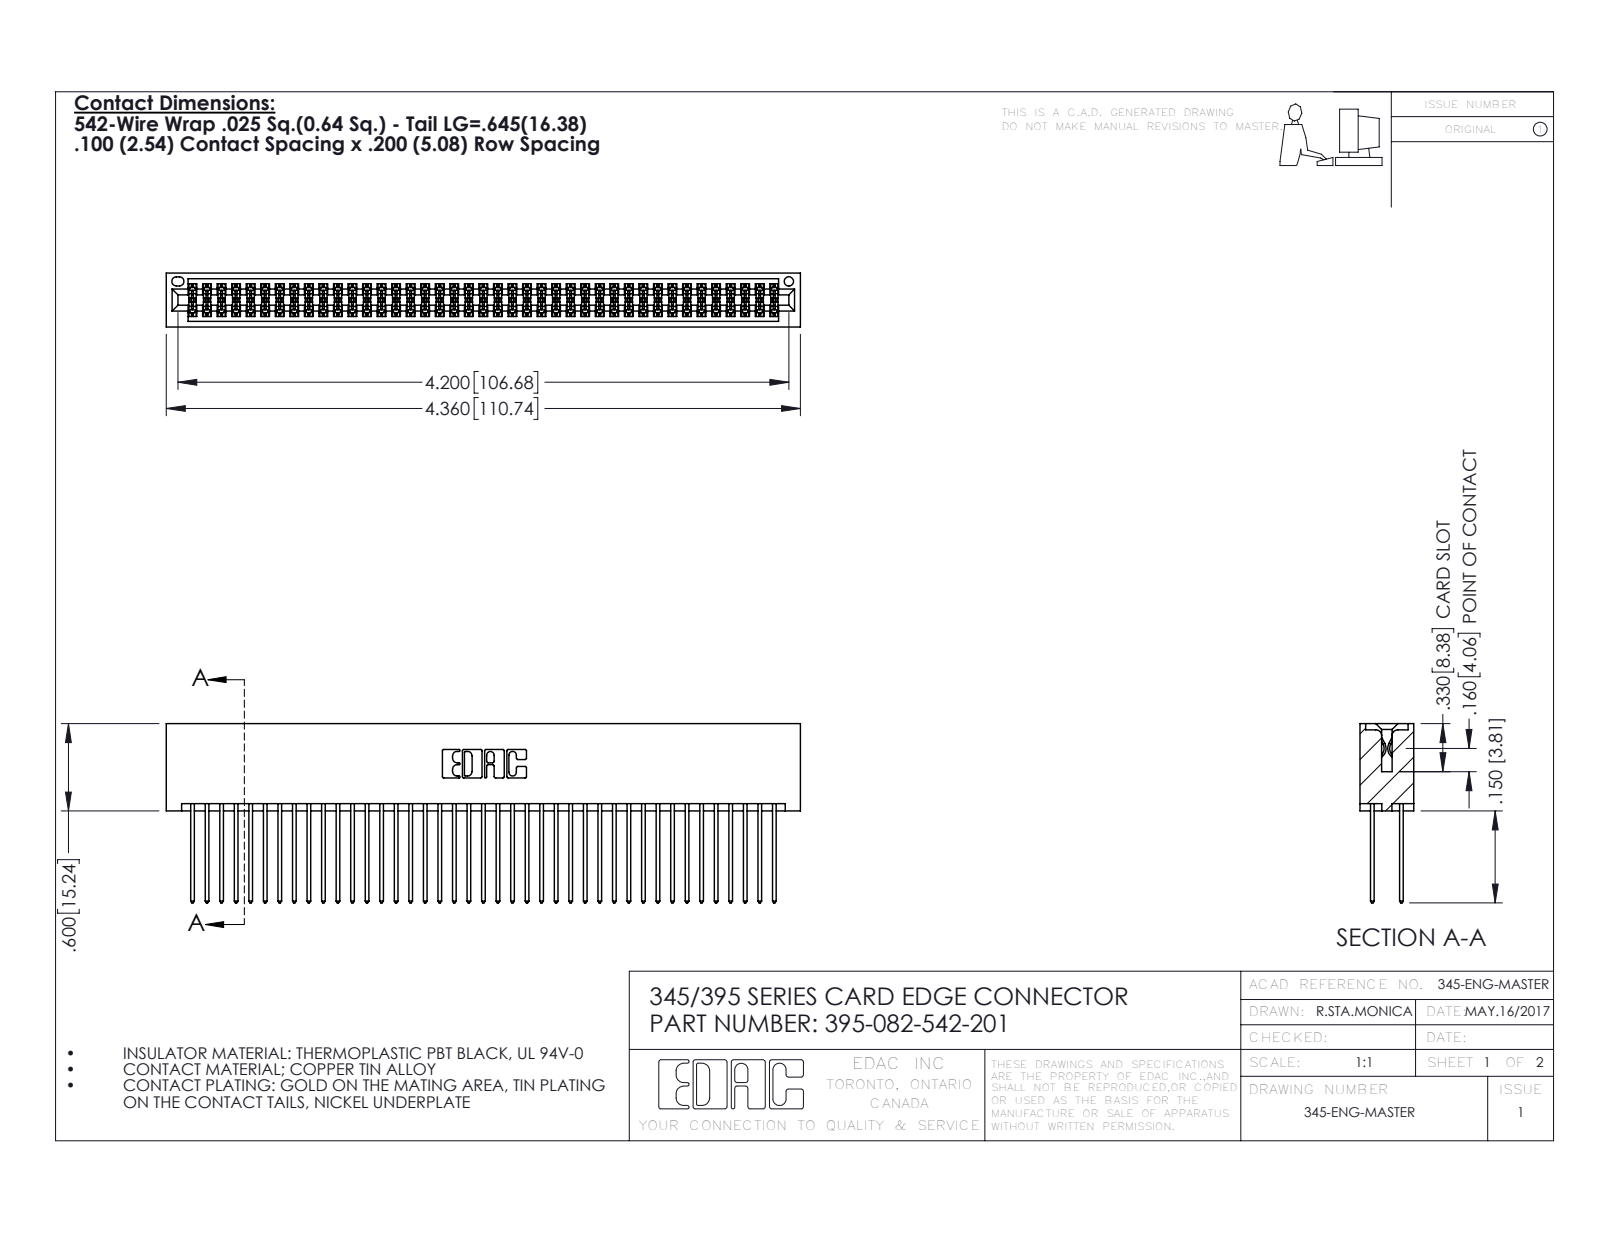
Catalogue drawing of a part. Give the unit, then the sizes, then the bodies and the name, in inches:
Units: inches
Overall size (bounding box): 4.36 × 1.232 × 0.37
Round holes (diameter × count): ⌀0.064 ×1
Partial cylindrical surfaces — rounded edges, fillets, slot ends (radius × count): R0.006 ×123, R0.01 ×82, R0.01 ×22, R0.007 ×6, R0.031 ×6, R0.026 ×3, R0.014 ×2, R0.019 ×2
Main face-to-face distances: 0.298, 0.072, 0.2, 0.098, 0.272, 0.025, 0.225, 0.37, 0.175, 0.149
Volume: 0.717 in³ · Surface area: 30.12 in²
Bodies: 83 solids, 4218 faces (2782 planar, 1436 cylindrical, 0 other)
Part name (STEP PRODUCT): 395-082-542-201; 345-292-001_345-293-142; 345 Part_No Mounting Lugs
STEP written by: SolidWorks 2016 (CONFIG_CONTROL_DESIGN)
